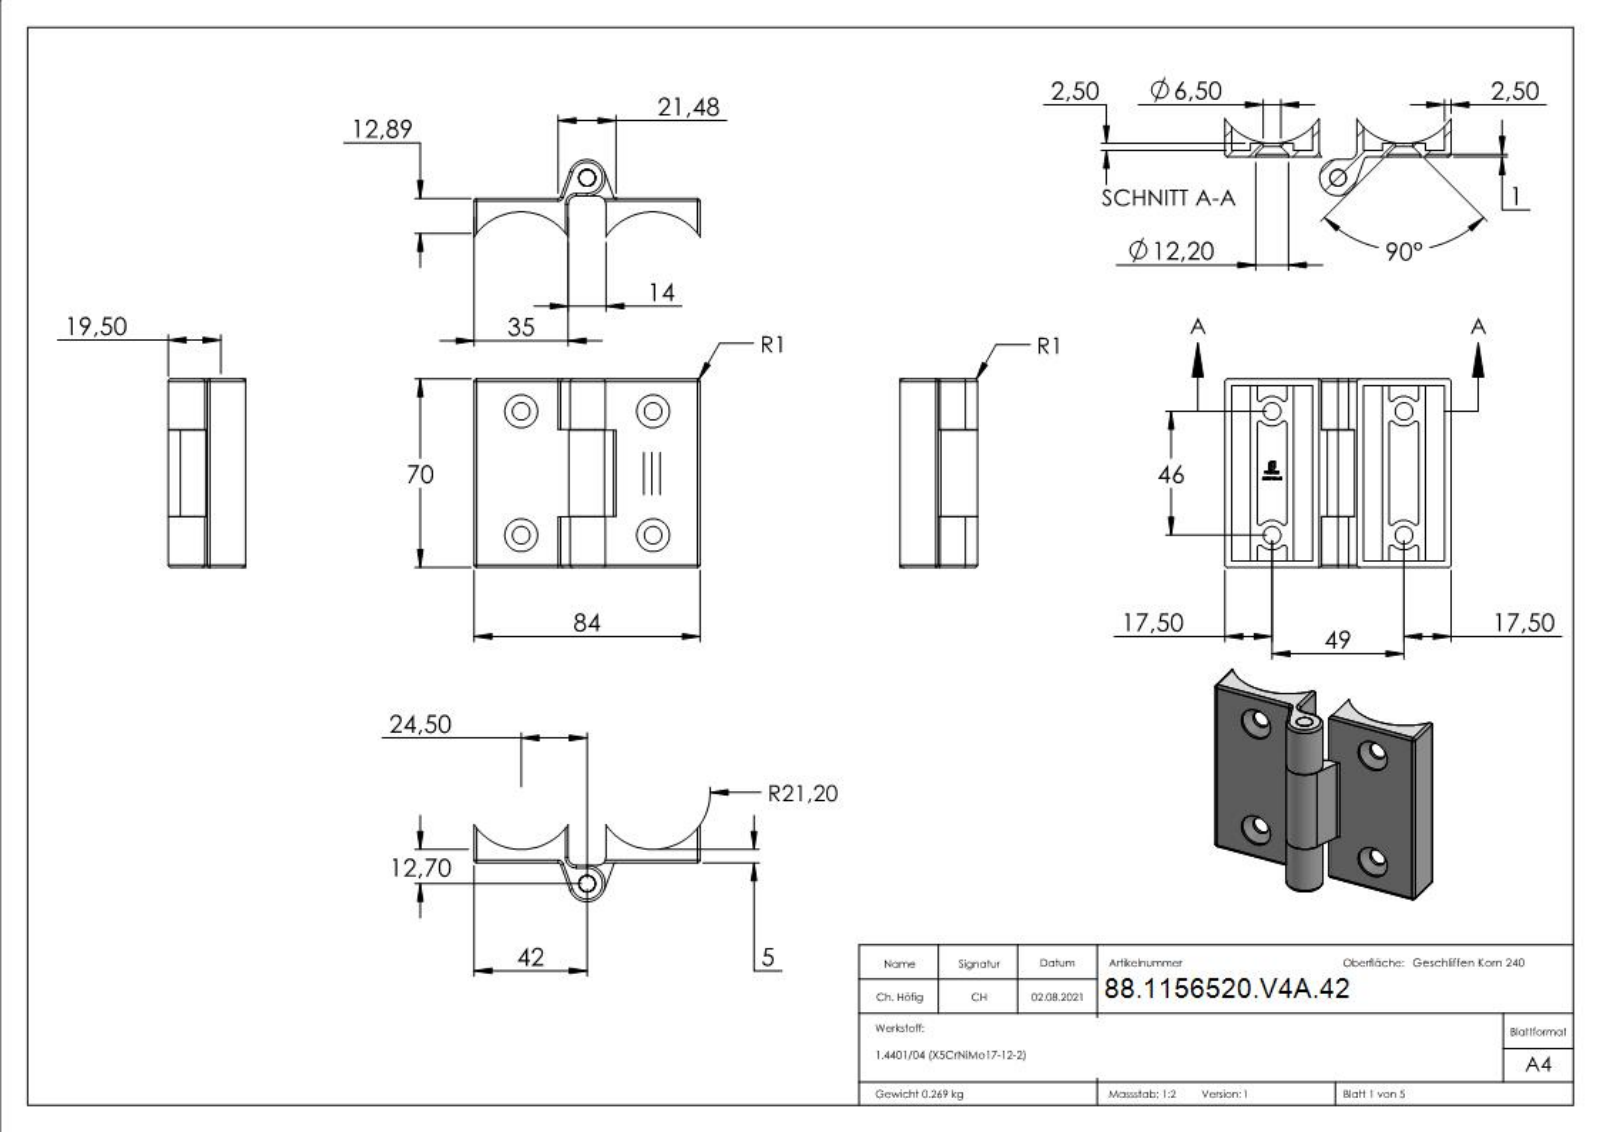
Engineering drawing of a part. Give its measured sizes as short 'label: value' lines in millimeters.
name: 5652X-V4A-XX Teil1; 5652X-V4A-XX Teil1_56520-V4A-42 Teil2; 5652X-V4A-XX Teil1_56520-V4A-42 Teil1; 56520-V4A-42 (+1 more)
written by: SolidWorks 2018 (CONFIG_CONTROL_DESIGN)
unit: mm
bodies: 3 solids, 752 faces (482 planar, 142 cylindrical, 128 other)
size: 84 × 70 × 28.73
volume: 33 677 mm³; area: 26 221 mm²
holes: 4× ⌀6.5, 4× ⌀12.2
bosses: 1× ⌀13.6, 1× ⌀6.2, 1× ⌀6
rounds: 32× R1, 4× R5.5, 2× R3, 2× R21.2
face distances: 2.5, 49, 32.5, 35, 16.5, 51.5, 46.5, 81.5, 30, 9.5
hole spacings: 46, 49, 67.21
